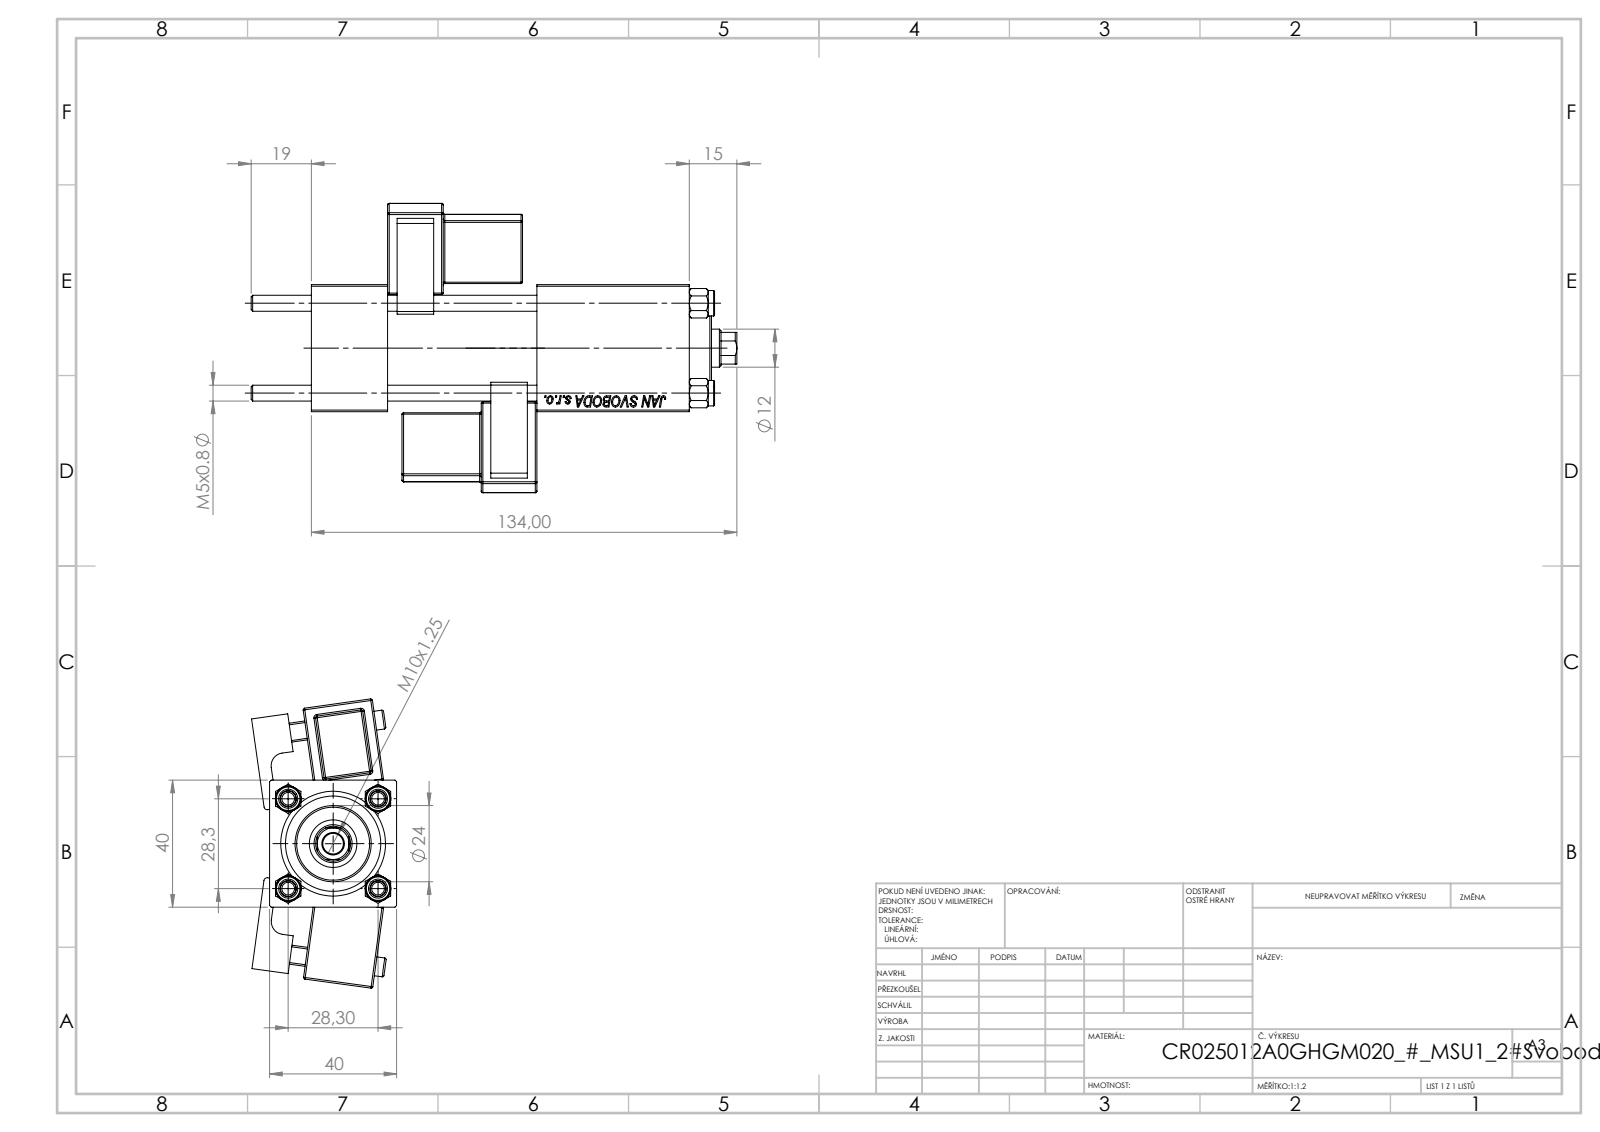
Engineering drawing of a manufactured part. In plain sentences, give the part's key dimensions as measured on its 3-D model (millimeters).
The part is named "V215_VC_A; V215CR_MSU; NUT_M5; V215CR_BODY_A (+2 more)". Its 3-D file was written by "SolidWorks 2019 (CONFIG_CONTROL_DESIGN)". It is 13 solids with 1289 faces: 579 planar, 138 cylindrical and 572 other. Overall it measures 153 by 91.08 by 45.69 millimeters. Its volume is 185 390 cubic millimeters and its surface area 70 830 square millimeters. Round holes: 4 of diameter 5, 3 of diameter 20, 2 of diameter 7, 2 of diameter 13.16, 1 of diameter 6.5, 1 of diameter 12, 1 of diameter 15, 1 of diameter 25, 1 of diameter 30. Round bosses or shafts: 4 of diameter 8, 2 of diameter 6, 1 of diameter 31, 1 of diameter 24. Partial cylindrical surfaces (rounded edges, fillets, slot ends): 48 of radius 0.5, 2 of radius 1, 2 of radius 2.5, 2 of radius 4, 1 of radius 5.5. The main face-to-face distances are 40, 24, 3, 71, 47, 20, 119, 95, 48, 90.3. The hole center spacings are 20.01, 28.3, 40.02, 72.
